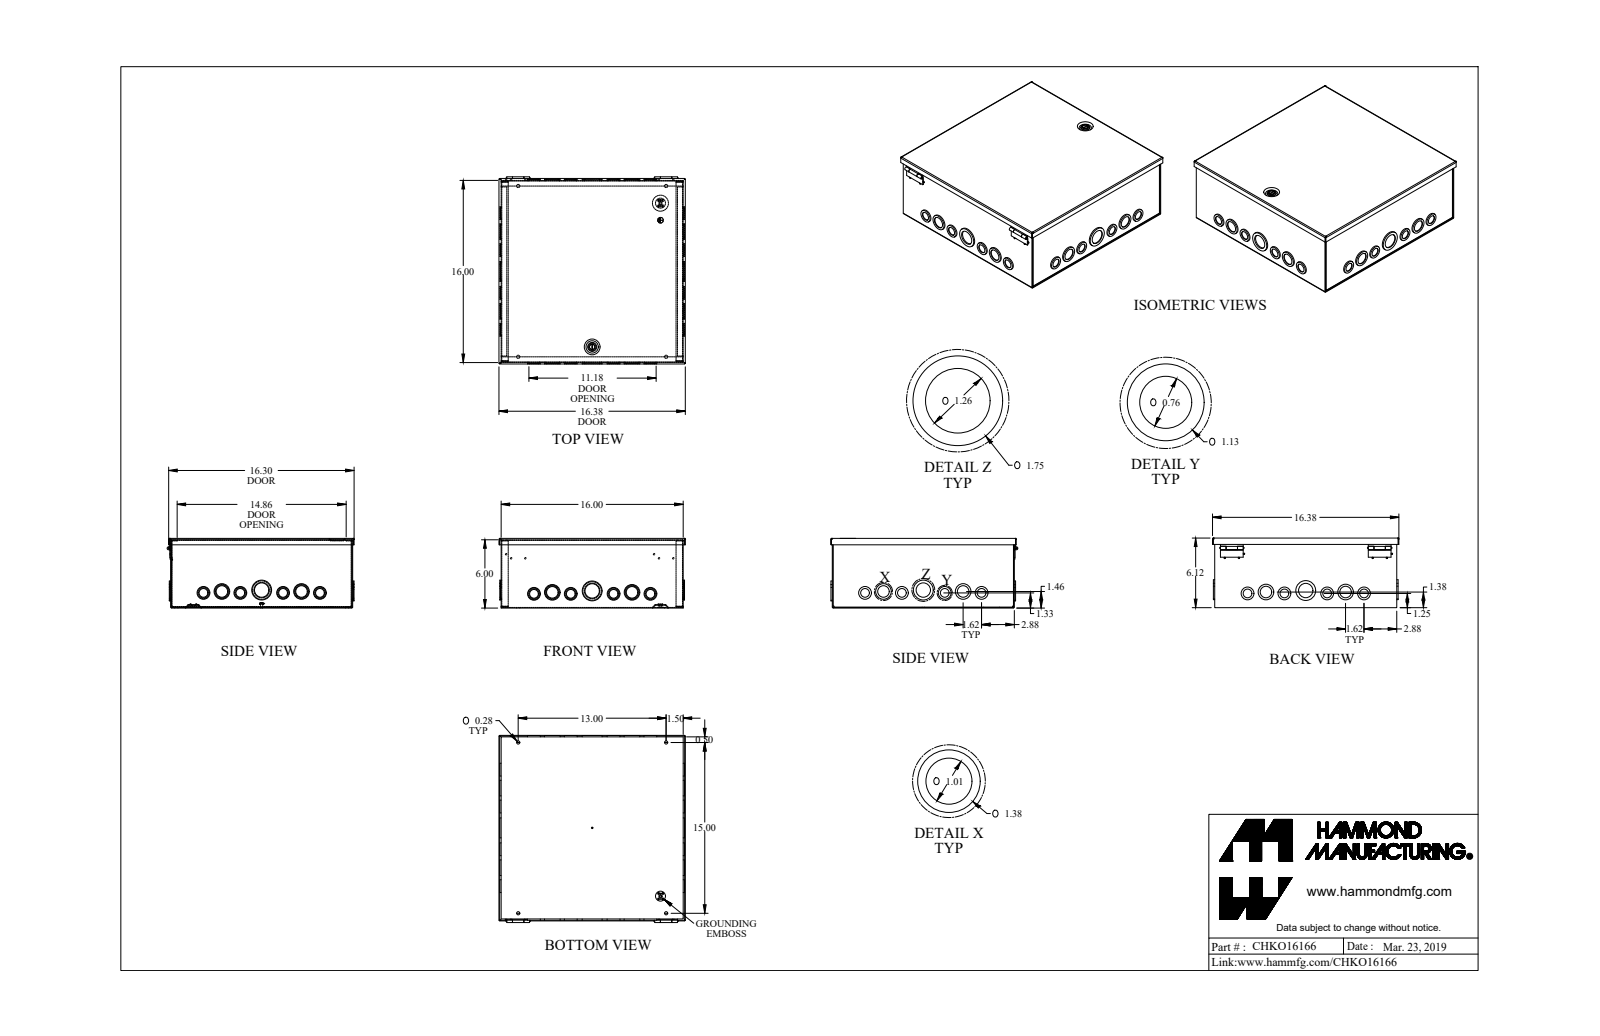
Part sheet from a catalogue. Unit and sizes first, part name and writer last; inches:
Units: inches
Overall size (bounding box): 16.443 × 16.38 × 6.118
Round holes (diameter × count): ⌀1.011 ×12, ⌀0.761 ×8, ⌀1.261 ×6, ⌀0.281 ×4, ⌀1.636 ×2, ⌀0.125 ×1, ⌀0.17 ×1, ⌀0.319 ×1, ⌀0.476 ×1, ⌀0.5 ×1
Round bosses / shafts (diameter × count): ⌀1.125 ×10, ⌀0.131 ×8, ⌀0.875 ×6, ⌀0.875 ×6, ⌀1.375 ×5, ⌀1.125 ×4, ⌀1.375 ×3, ⌀1.75 ×2
Partial cylindrical surfaces — rounded edges, fillets, slot ends (radius × count): R0.029 ×16, R0.086 ×16, R0.057 ×8, R0.012 ×4, R0.1 ×4, R0.036 ×2, R0.079 ×2, R0.25 ×2
Main face-to-face distances: 0.057, 6.061, 15.943, 6.118, 6.004, 16, 15.886, 5.943, 0.118, 0.08
Hole centre spacings: 1.625, 7, 1.896, 3.24, 3.502, 5.126, 5.381, 8.621
Volume: 58.24 in³ · Surface area: 2 052 in²
Bodies: 12 solids, 823 faces (384 planar, 396 cylindrical, 43 other)
Part name (STEP PRODUCT): CHKO16166_Default
STEP written by: SolidWorks 2019 (CONFIG_CONTROL_DESIGN)
